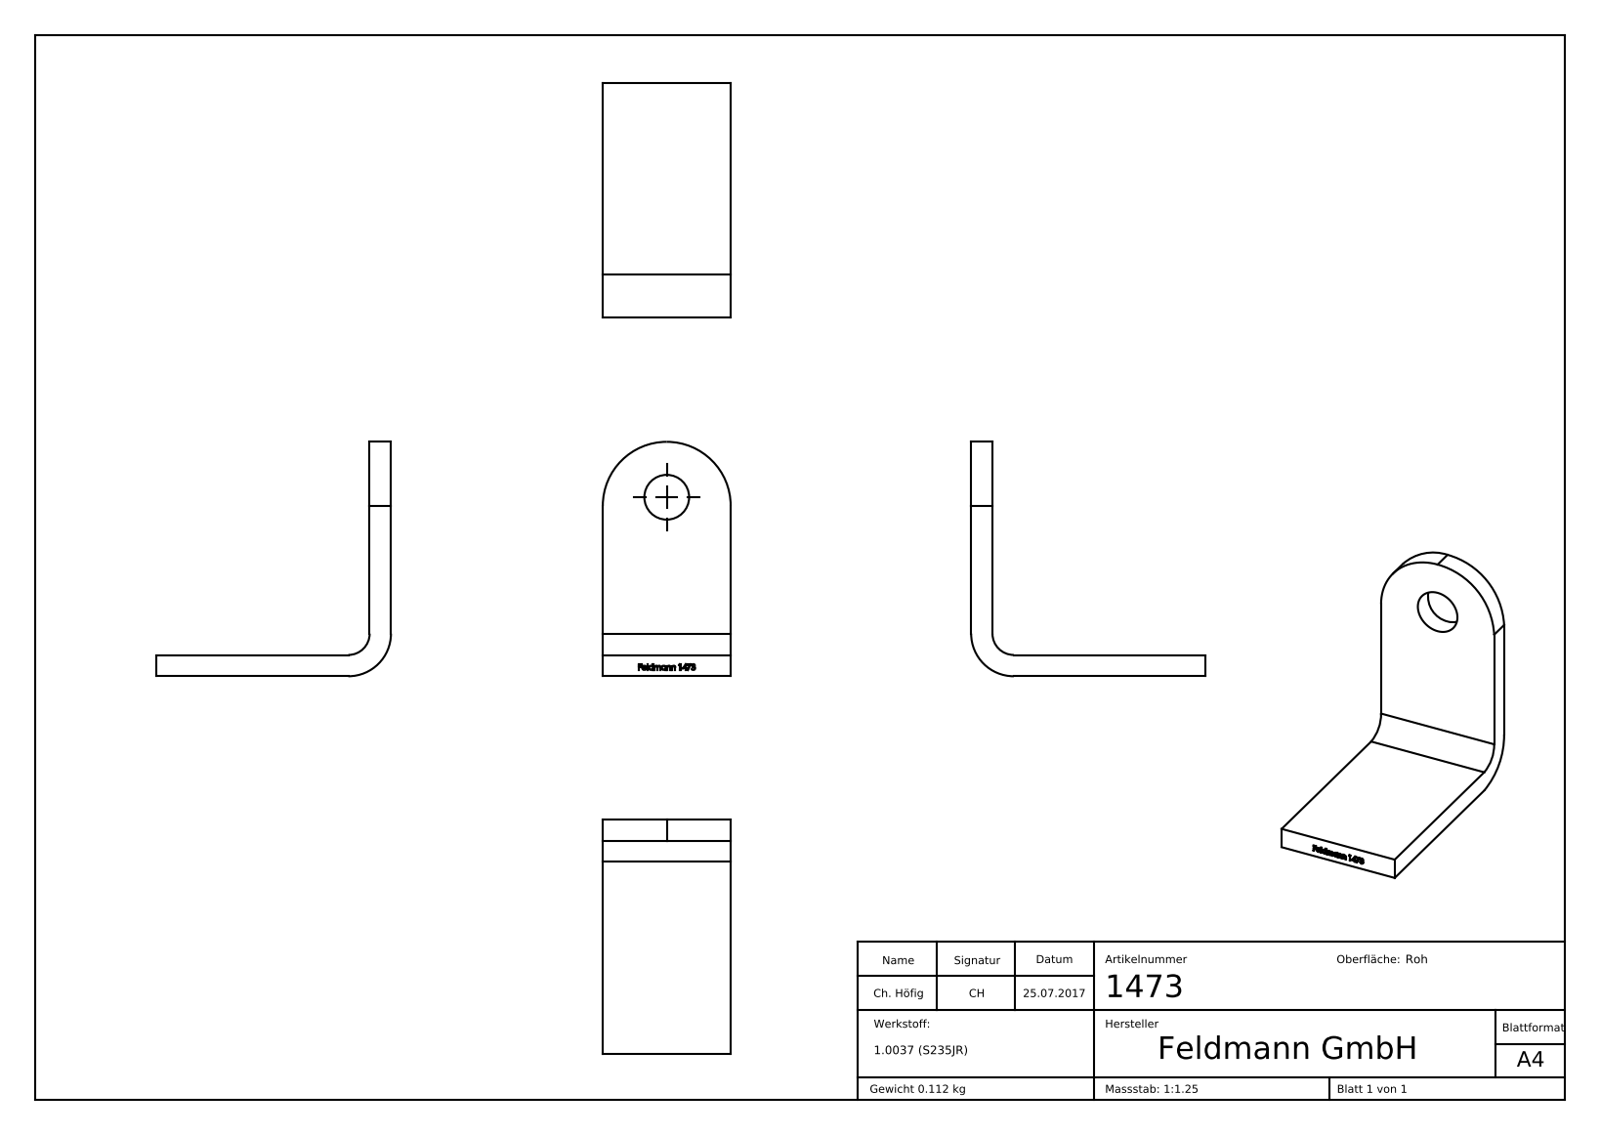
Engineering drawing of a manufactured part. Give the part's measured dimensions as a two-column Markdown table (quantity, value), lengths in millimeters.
| quantity | value |
| --- | --- |
| part name | 1473 |
| STEP written by | SolidWorks 2015 (CONFIG_CONTROL_DESIGN) |
| units | millimeters |
| bodies | 1 solid, 173 faces (105 planar, 6 cylindrical, 62 other) |
| overall size | 55 × 55 × 30 |
| volume | 14 351 mm³ |
| surface area | 7 166 mm² |
| round holes (diameter × count) | 10.5 × 1 |
| partial cylindrical surfaces (radius × count) | 5 × 1, 10 × 1, 15 × 1 |
| main face-to-face distances | 5, 30, 55, 50, 54.9, 49.9, 3.19, 1.24, 0.39, 2.97 |
